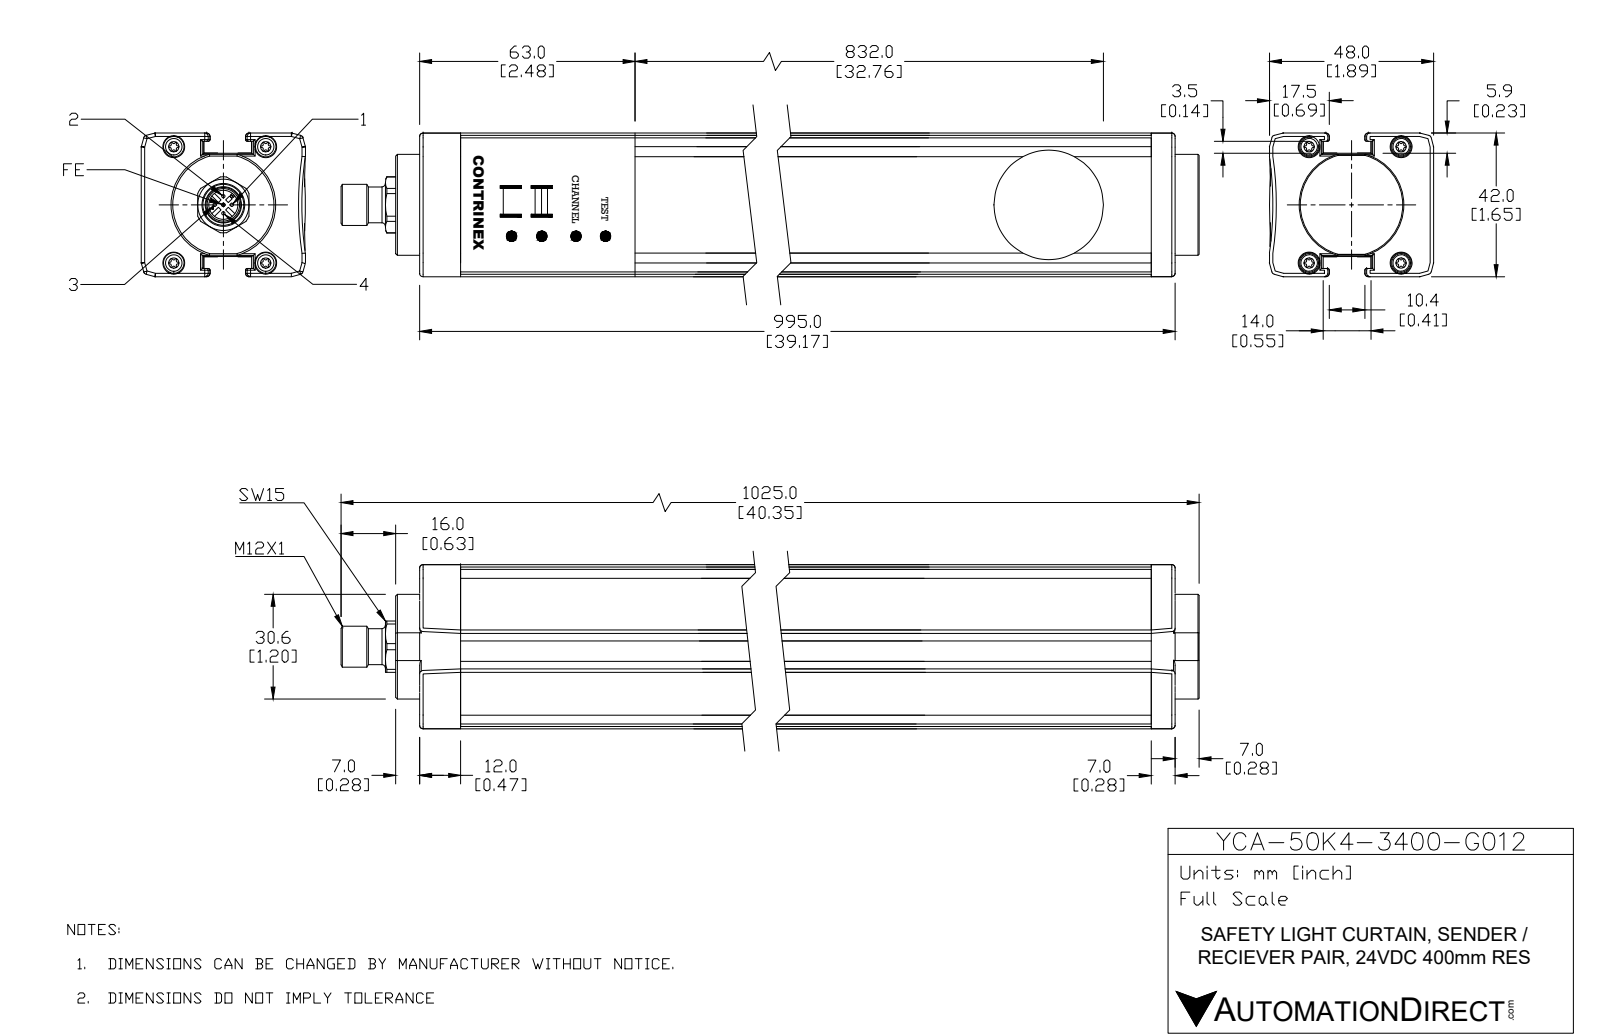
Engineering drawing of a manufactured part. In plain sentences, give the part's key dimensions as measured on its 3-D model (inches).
The part is named "YCA-50K4-3400-G012". Its 3-D file was written by "SolidWorks 2019 (AUTOMOTIVE_DESIGN)". It is 1 solid with 533 faces: 121 planar, 152 cylindrical and 260 other. Overall it measures 40.355 by 1.89 by 1.654 inches. Its volume is 102.4 cubic inches and its surface area 452.2 square inches. Round holes: 4 of diameter 0.12, 4 of diameter 0.236, 1 of diameter 0.335. Round bosses or shafts: 5 of diameter 0.039, 4 of diameter 0.217, 4 of diameter 0.119, 1 of diameter 1.205, 1 of diameter 0.472, 1 of diameter 0.413. Partial cylindrical surfaces (rounded edges, fillets, slot ends): 36 of radius 0.035, 12 of radius 0.039, 10 of radius 0.016, 2 of radius 0.217, 1 of radius 0.02, 1 of radius 0.02, 1 of radius 0.323, 1 of radius 0.689. The main face-to-face distances are 0.231, 1.422, 1.654, 1.191, 1.827, 2.172, 2.005, 0.2, 1.454, 0.031. The hole center spacings are 0.828, 0.88, 1.059, 1.339, 1.707.
